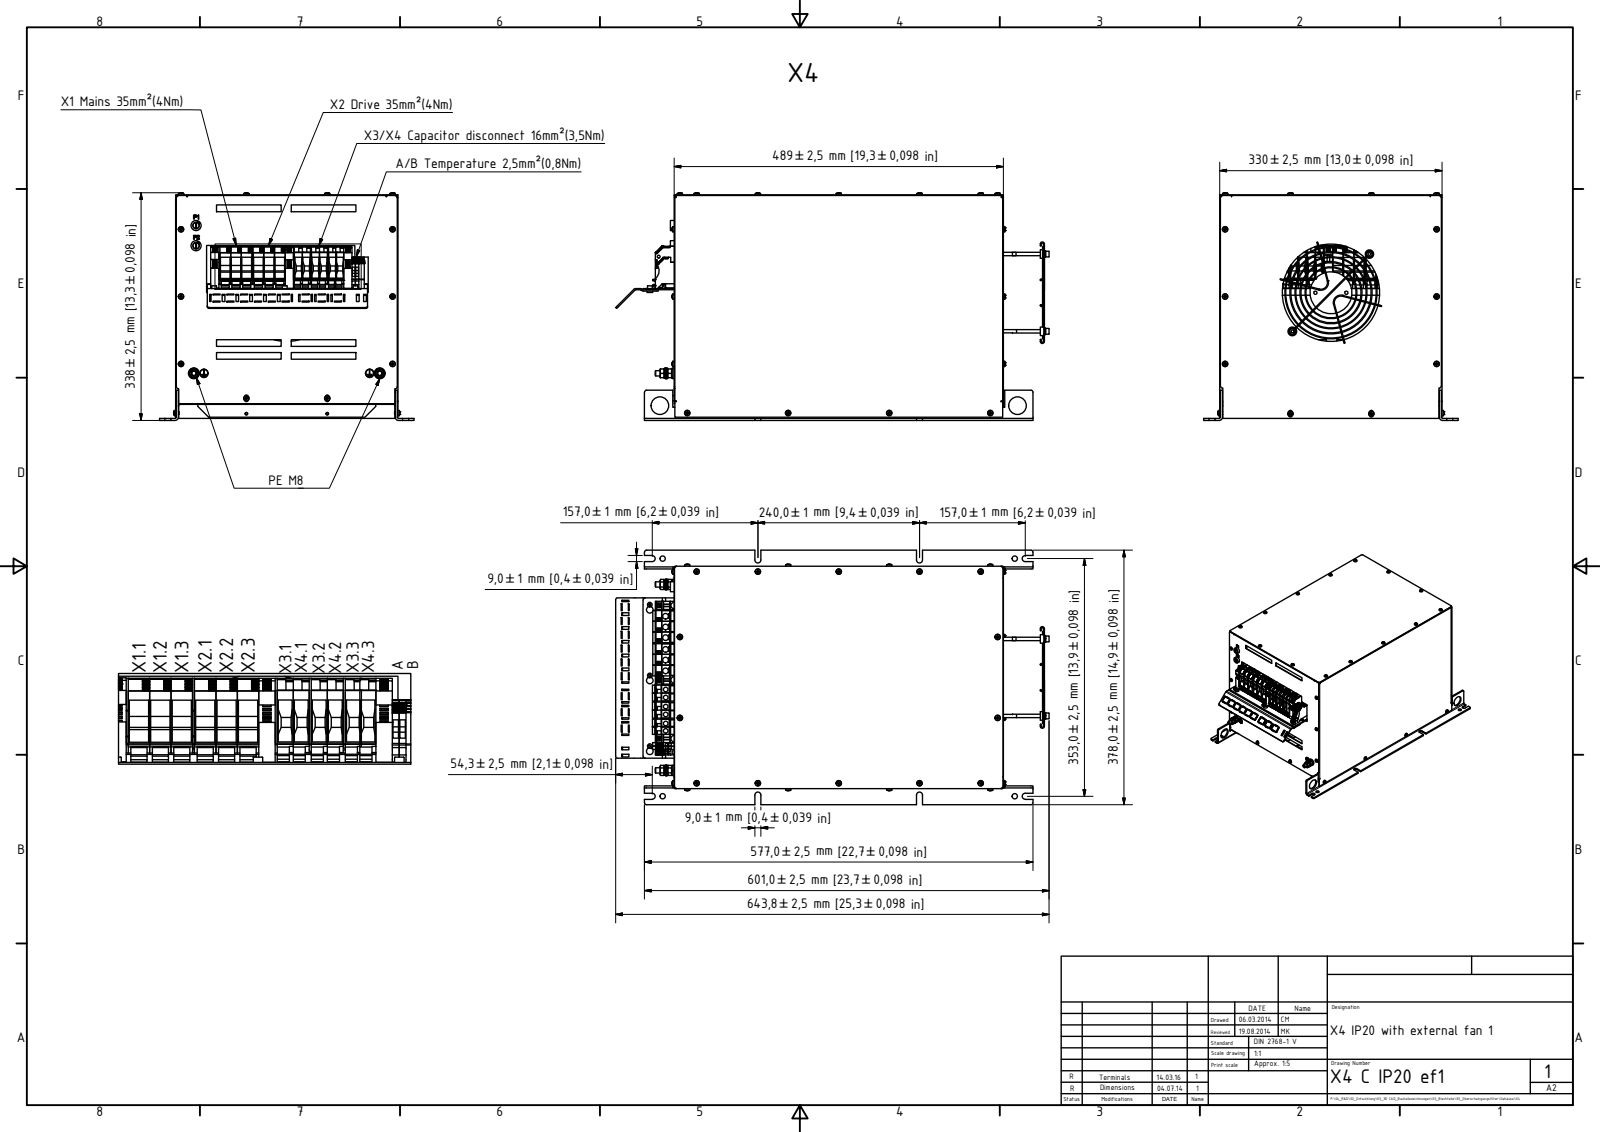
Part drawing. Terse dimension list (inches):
name: 10100257 Bodenblech X4; 10100395 Seitenwand RHF-BG X4-A; 10100394 Lüfterblech RHF-BG X4-A; 10100393 Deckel RHF-BG X4-A (+8 more)
written by: Autodesk Inventor 2015 (AUTOMOTIVE_DESIGN)
unit: in
bodies: 116 solids, 8827 faces (5326 planar, 2658 cylindrical, 843 other)
size: 25.345 × 14.882 × 13.315
volume: 115.5 in³; area: 3 557 in²
holes: 35× ⌀0.128, 29× ⌀0.197, 19× ⌀0.268, 12× ⌀0.325, 10× ⌀0.315, 6× ⌀0.276, 5× ⌀0.157, 5× ⌀0.236, 4× ⌀0.167, 3× ⌀0.156, 3× ⌀0.37, 3× ⌀0.394
bosses: 31× ⌀0.157, 28× ⌀0.144, 8× ⌀0.055, 5× ⌀0.335, 4× ⌀0.63, 4× ⌀0.449, 4× ⌀0.362, 3× ⌀0.276
rounds: 112× R0.028, 109× R0.02, 61× R0.004, 60× R0.039, 58× R0.006, 41× R0.004, 41× R0.079, 35× R0.008
face distances: 0.039, 12.953, 12.992, 12.913, 19.213, 0.118, 12.205, 12.244, 12.087, 12.126
hole spacings: 0.827, 4.724, 12.362, 1.432, 1.063, 1.811, 1.969, 2.131
